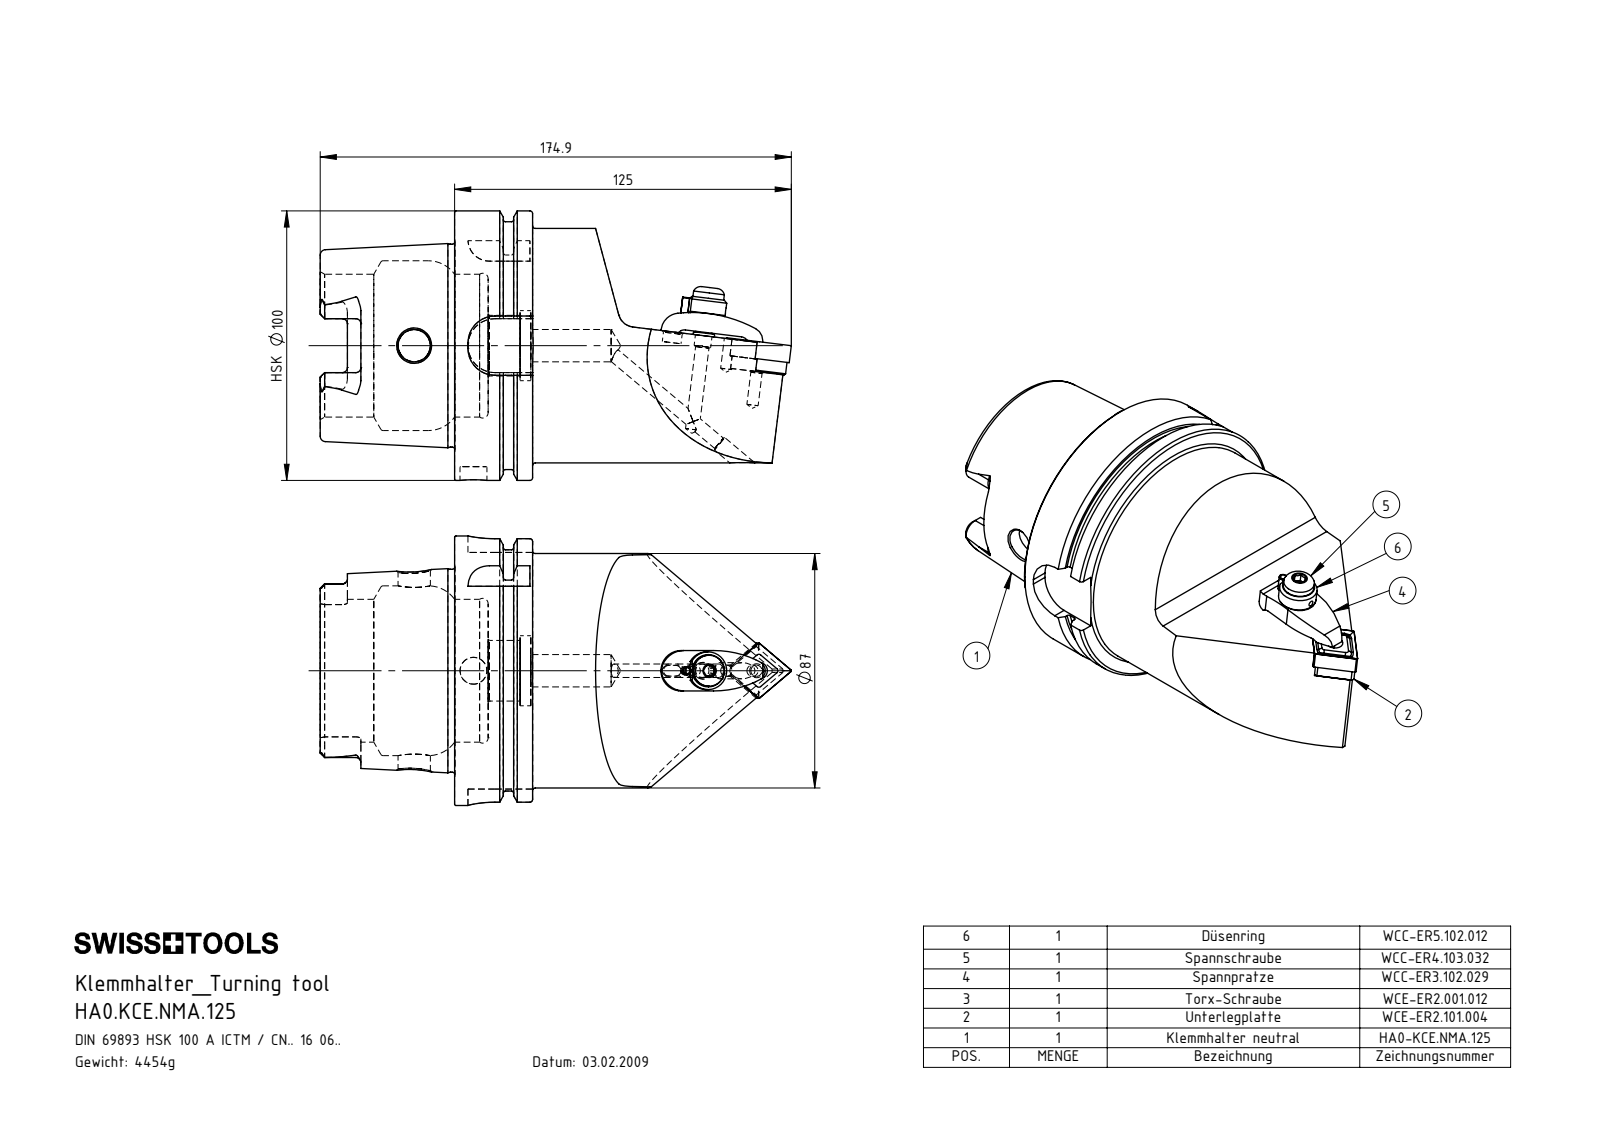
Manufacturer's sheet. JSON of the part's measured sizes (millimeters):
{"part_name": "WCC-ER3.102.029_C; WCC-ER4.103.032_A; HA0-KCE.NMA.125_A; WCC-ER5.102.012_B (+7 more)", "step_written_by": "SolidWorks 2017 (AUTOMOTIVE_DESIGN)", "units": "millimeters", "bodies": {"solids": 11, "faces": 455, "planar": 120, "cylindrical": 151, "other": 184}, "overall_size": [174.9, 100, 100], "volume_mm3": 566305, "surface_area_mm2": 75091, "round_holes": [[2, 3], [5, 3], [4.2, 2], [7, 2], [12, 2], [2.4, 1], [3, 1], [6, 1], [6.2, 1], [6.35, 1], [7.9, 1], [8.5, 1]], "round_bosses_or_shafts": [[6, 2], [3, 2], [100, 1], [91.95, 1], [87, 1], [75.26, 1], [14, 1], [11.5, 1]], "partial_cylinders_radius": [[0.45, 6], [1.9, 6], [0.4, 4], [0.79, 4], [1, 4], [1.5, 3], [10, 3], [0.79, 2]], "face_to_face_distances": [12.45, 28.95, 16.5, 49.9, 62.35, 78.85, 87.8, 78.2, 28.3, 15.85], "hole_center_spacings": [7.99, 8, 8.2, 17.8, 21.1, 21.11, 29.1, 0.5]}
